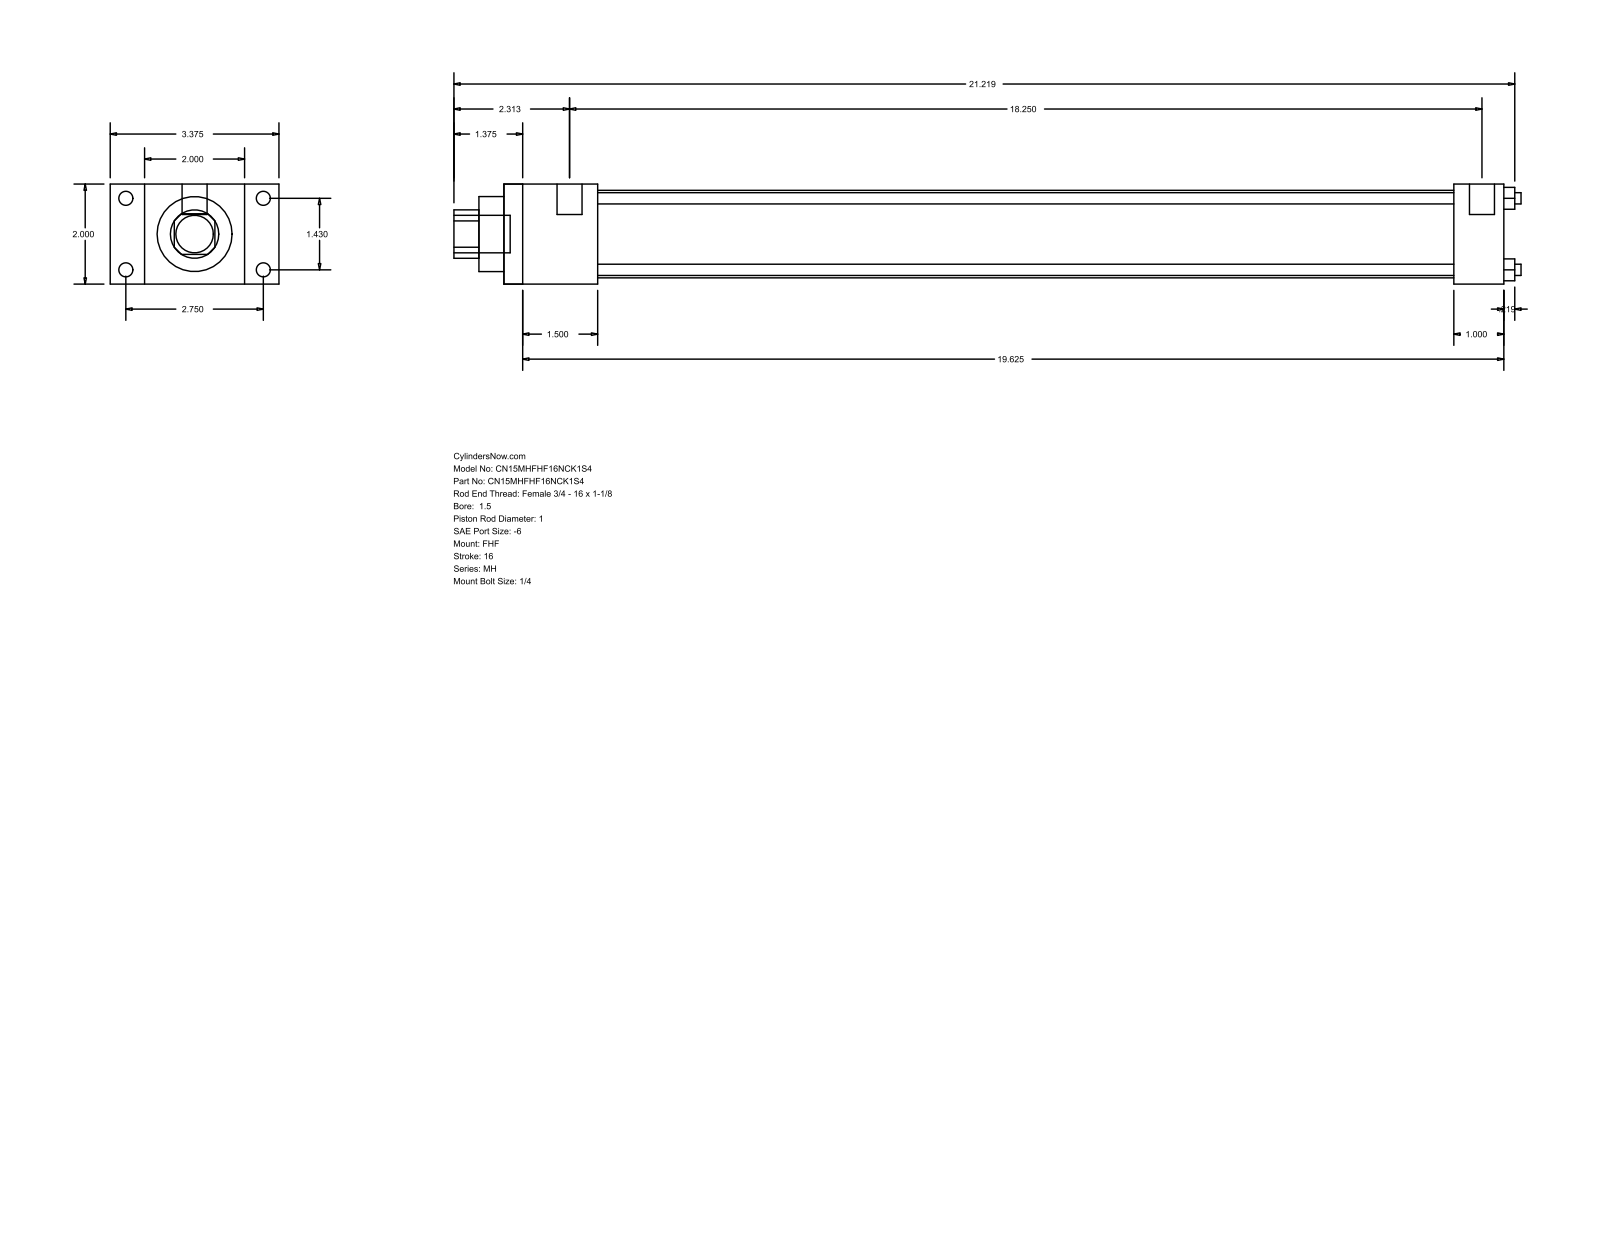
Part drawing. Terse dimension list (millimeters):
name: MH_FHF__0150_1
written by: GSSL Pune (CONFIG_CONTROL_DESIGN)
unit: mm
bodies: 0 solids, 88 faces (60 planar, 28 cylindrical, 0 other)
size: 542.13 × 85.72 × 50.8
holes: 4× ⌀5.71, 1× ⌀25.4, 1× ⌀38.1, 1× ⌀44.45
bosses: 4× ⌀7.14, 4× ⌀5.56, 2× ⌀12.7, 1× ⌀19.05
rounds: 1× R12.29
face distances: 50.8, 17.46, 68.26, 47.63, 85.72, 508, 460.37, 25.4, 482.6, 434.97
hole spacings: 25.68, 36.32, 51.36
